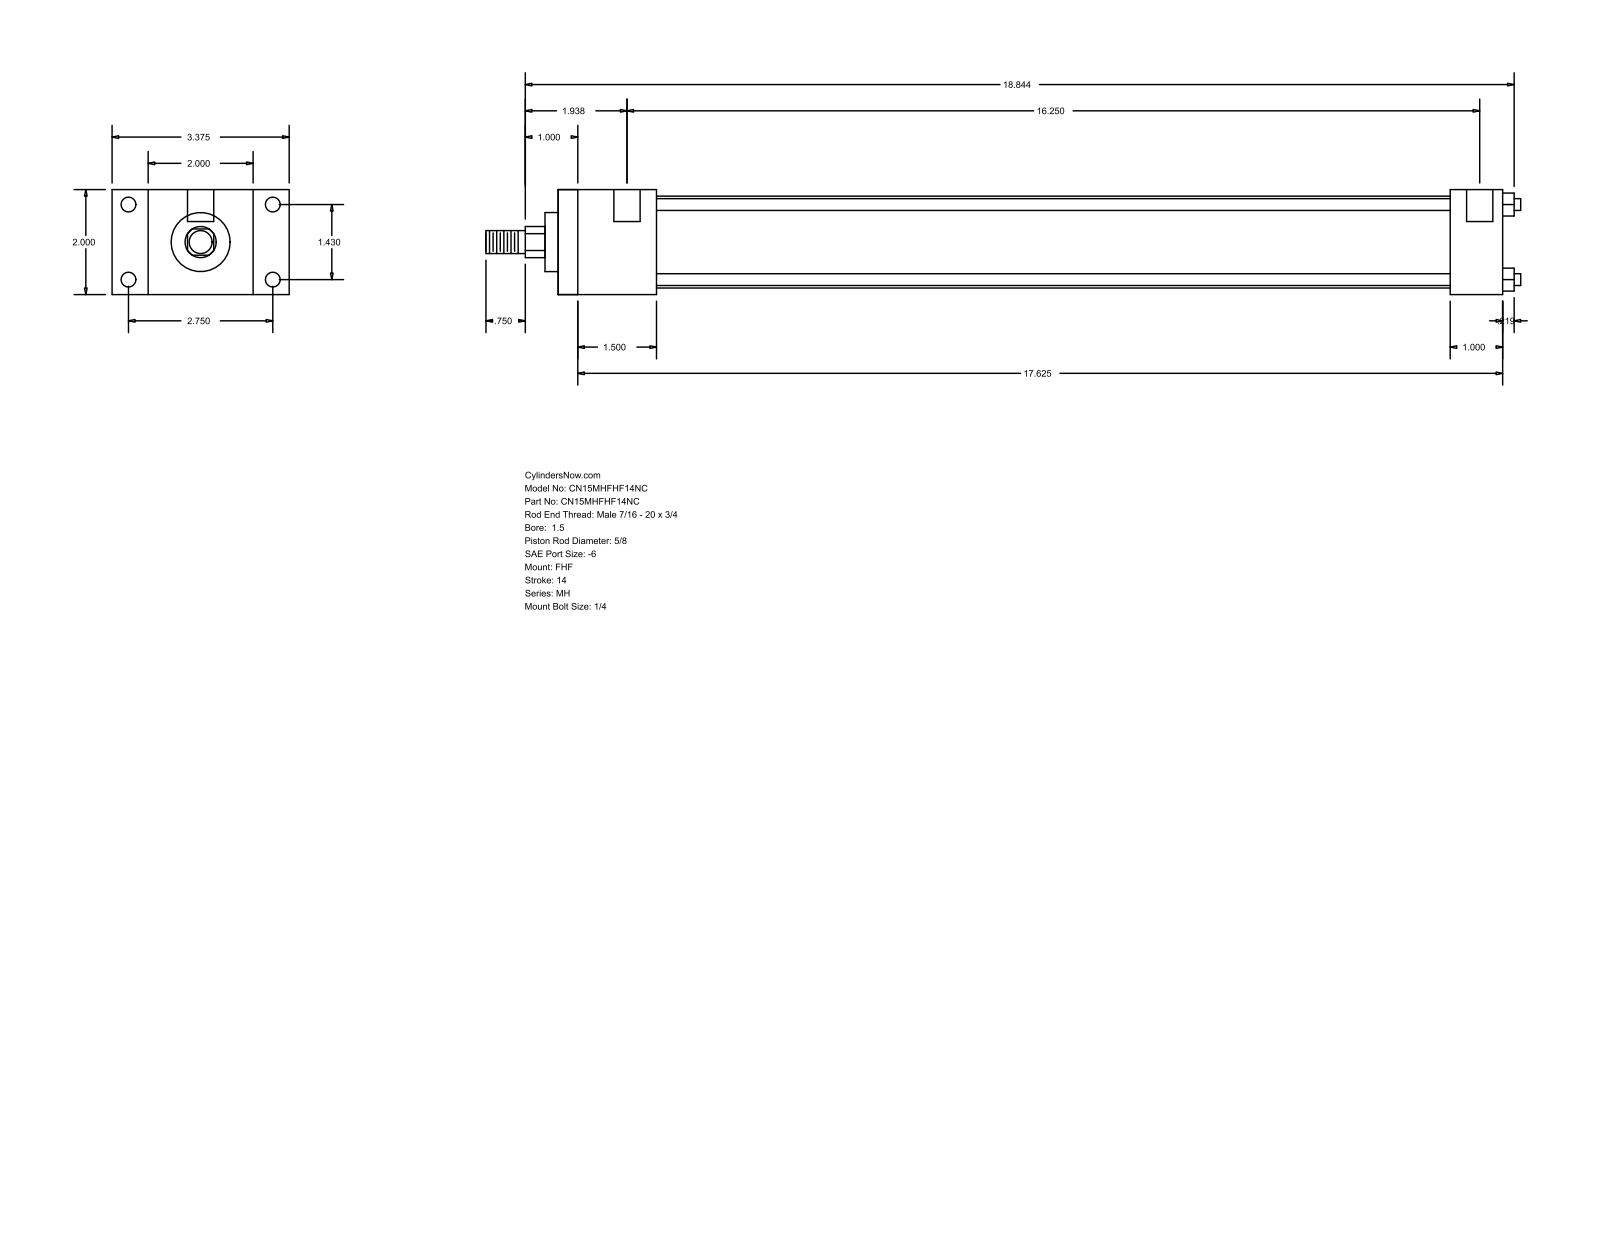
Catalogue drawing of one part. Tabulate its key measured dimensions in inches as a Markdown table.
| quantity | value |
| --- | --- |
| part name | MH_FHF__0150_0.625 |
| STEP written by | GSSL Pune (CONFIG_CONTROL_DESIGN) |
| units | inches |
| bodies | 0 solids, 88 faces (60 planar, 28 cylindrical, 0 other) |
| overall size | 19.719 × 3.375 × 2 |
| round holes (diameter × count) | 0.219 × 4, 0.281 × 4, 0.5 × 2 |
| round bosses / shafts (diameter × count) | 0.225 × 4, 1.75 × 1, 1.125 × 1, 0.625 × 1, 0.437 × 1 |
| partial cylindrical surfaces (radius × count) | 0.297 × 1 |
| main face-to-face distances | 2, 0.687, 2.687, 1.875, 3.375, 18, 16.125, 17, 15.125, 1 |
| hole center spacings | 1.43, 2.75, 3.099, 16.375, 0.125, 16.25 |
